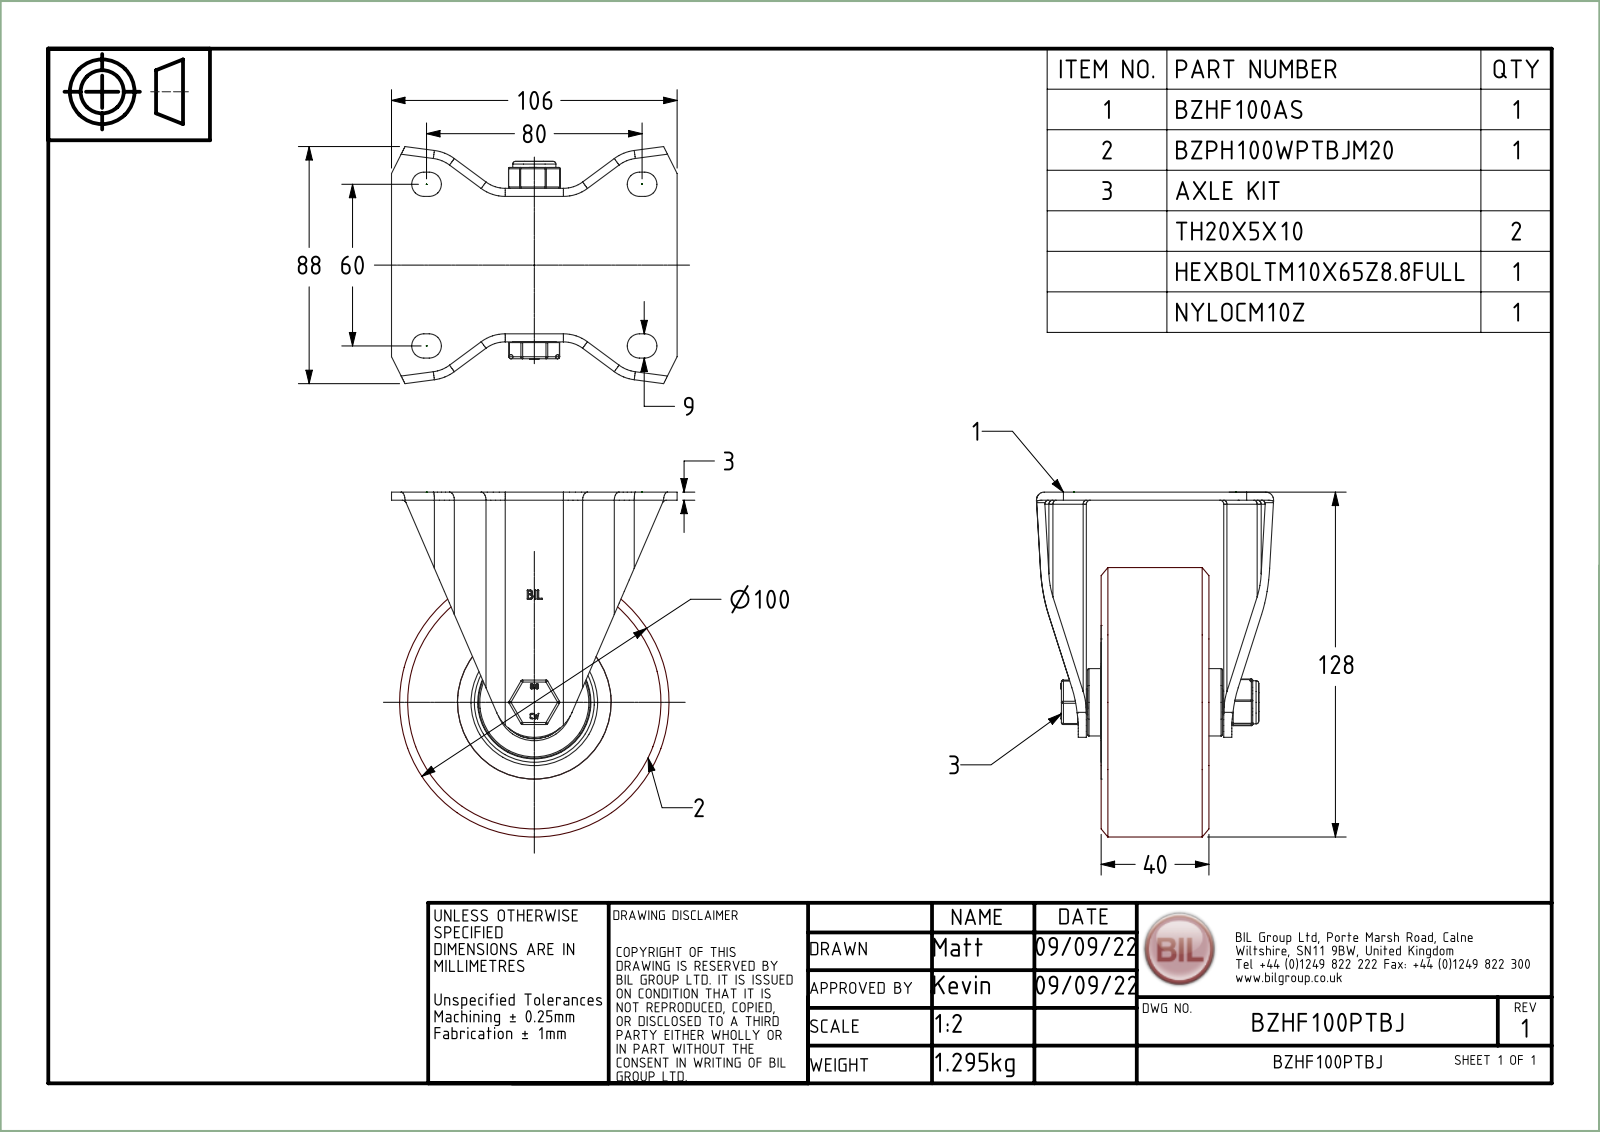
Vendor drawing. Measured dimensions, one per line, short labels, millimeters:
name: BZHF100AS; ZINC PLATED, PRESSED STEEL BRACKET; BZHF100PTBJ; BZPH100WPTBJM20 (+7 more)
written by: Spatial InterOp 3D (AUTOMOTIVE_DESIGN)
unit: mm
bodies: 35 solids, 1594 faces (598 planar, 502 cylindrical, 494 other)
size: 128 × 106 × 88
volume: 355 894 mm³; area: 131 033 mm²
holes: 1× ⌀10, 1× ⌀10.25, 1× ⌀10.5, 1× ⌀12, 1× ⌀20, 1× ⌀28.5, 1× ⌀30, 1× ⌀41.5, 1× ⌀42, 1× ⌀44, 1× ⌀47, 1× ⌀57
bosses: 1× ⌀100, 1× ⌀40.5, 1× ⌀40, 1× ⌀29, 1× ⌀27, 1× ⌀25, 1× ⌀24, 1× ⌀19.85
rounds: 20× R6, 18× R0.5, 16× R4, 12× R0.75, 12× R1.5, 10× R3, 8× R4.5, 4× R8
face distances: 3, 40, 26, 5.5, 45.5, 19.5, 13.5, 8.5, 48.5, 54
